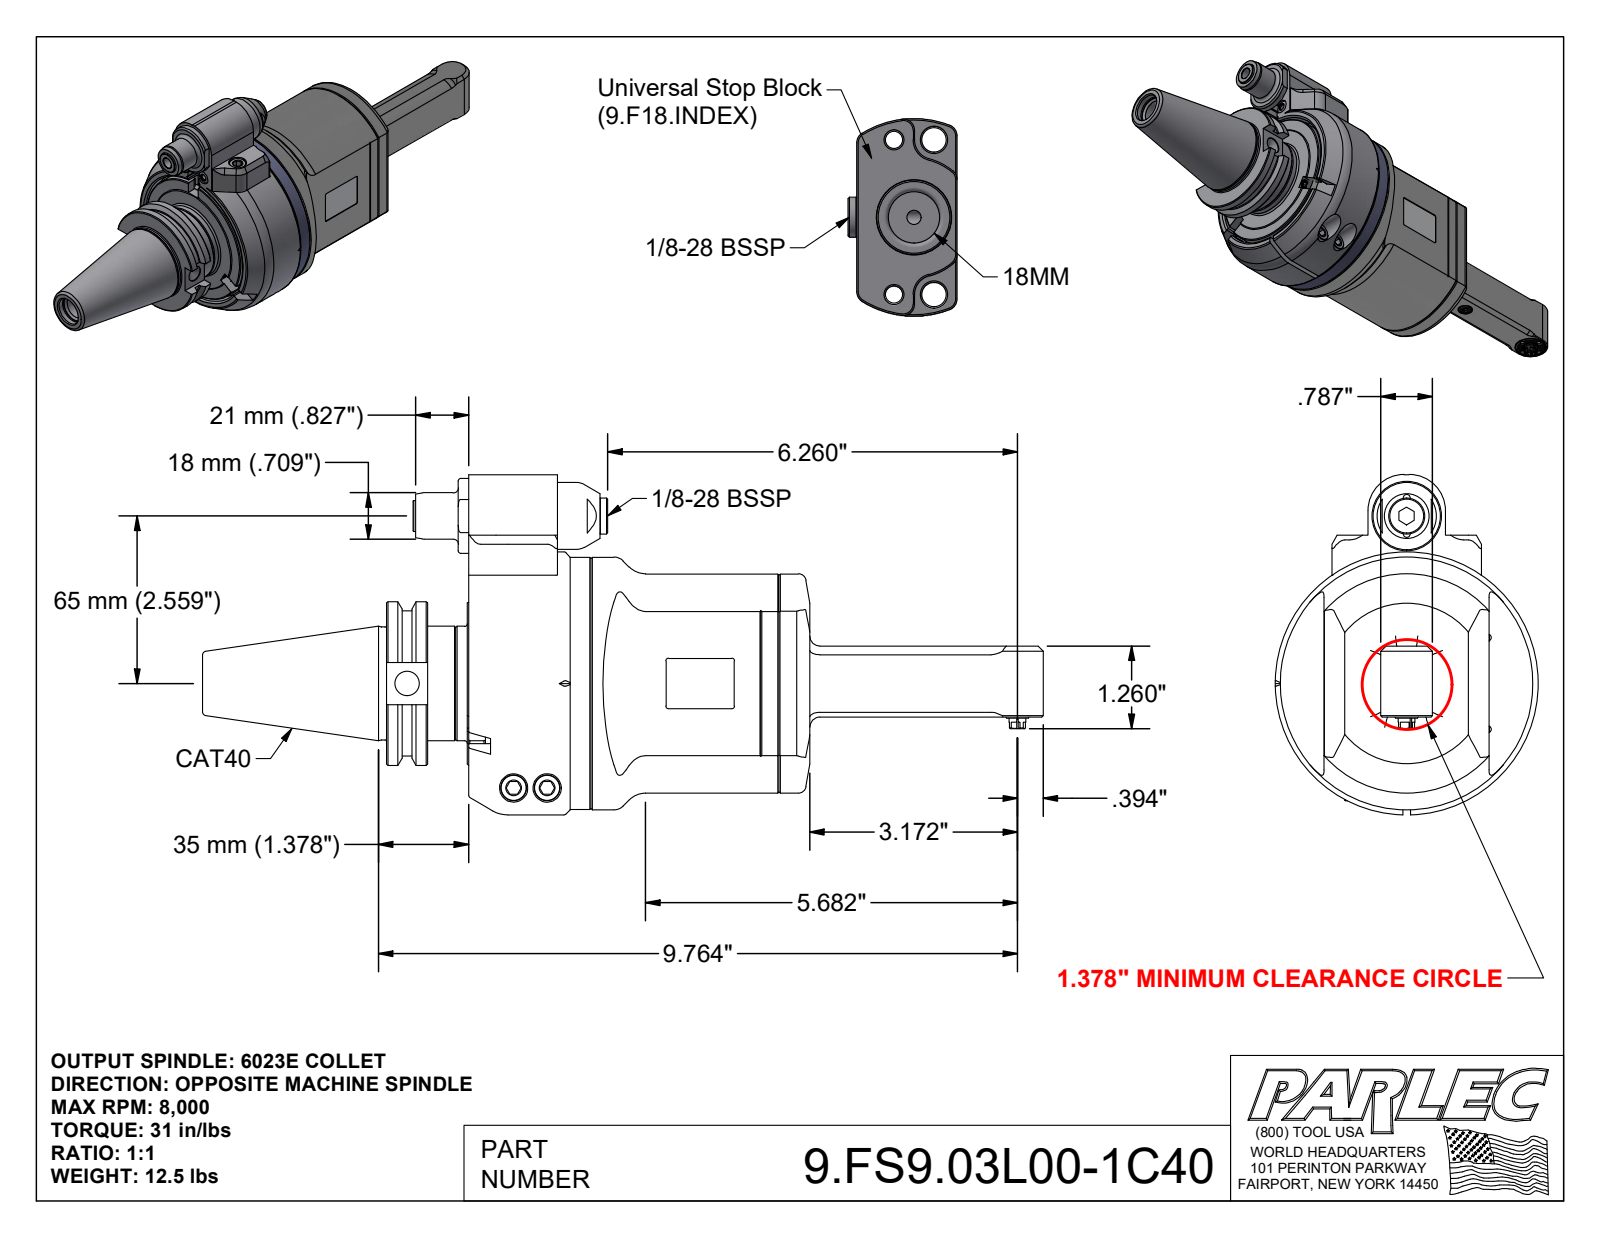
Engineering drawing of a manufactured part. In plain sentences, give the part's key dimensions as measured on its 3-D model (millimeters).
The part is named "9.FS9.03L00-1C40; 9_FS9_03L00; 9_GA". Its 3-D file was written by "Autodesk Inventor 2025 (AUTOMOTIVE_DESIGN)". It is 4 solids with 638 faces: 293 planar, 173 cylindrical and 172 other. Overall it measures 326.2 by 132 by 102 millimeters. Its volume is 1 011 000 cubic millimeters and its surface area 143 200 square millimeters. Round holes: 6 of diameter 2.6, 4 of diameter 3.2, 3 of diameter 5, 3 of diameter 6.5, 2 of diameter 3, 2 of diameter 3.3, 2 of diameter 4.2, 2 of diameter 8, 2 of diameter 8.5, 2 of diameter 10.4, 2 of diameter 11, 2 of diameter 12.5. Round bosses or shafts: 4 of diameter 10, 3 of diameter 8, 2 of diameter 18, 2 of diameter 12, 2 of diameter 9, 2 of diameter 6, 2 of diameter 2.5, 1 of diameter 102. Partial cylindrical surfaces (rounded edges, fillets, slot ends): 18 of radius 1, 10 of radius 4, 8 of radius 2, 6 of radius 3, 2 of radius 0.5, 2 of radius 8, 2 of radius 14, 1 of radius 2.5. The main face-to-face distances are 8.5, 35, 7, 22, 42, 2, 0.5, 5, 64, 39.5. The hole center spacings are 6.8, 8.3, 9.6, 11.7, 7, 12.8, 13.5, 16.5.
